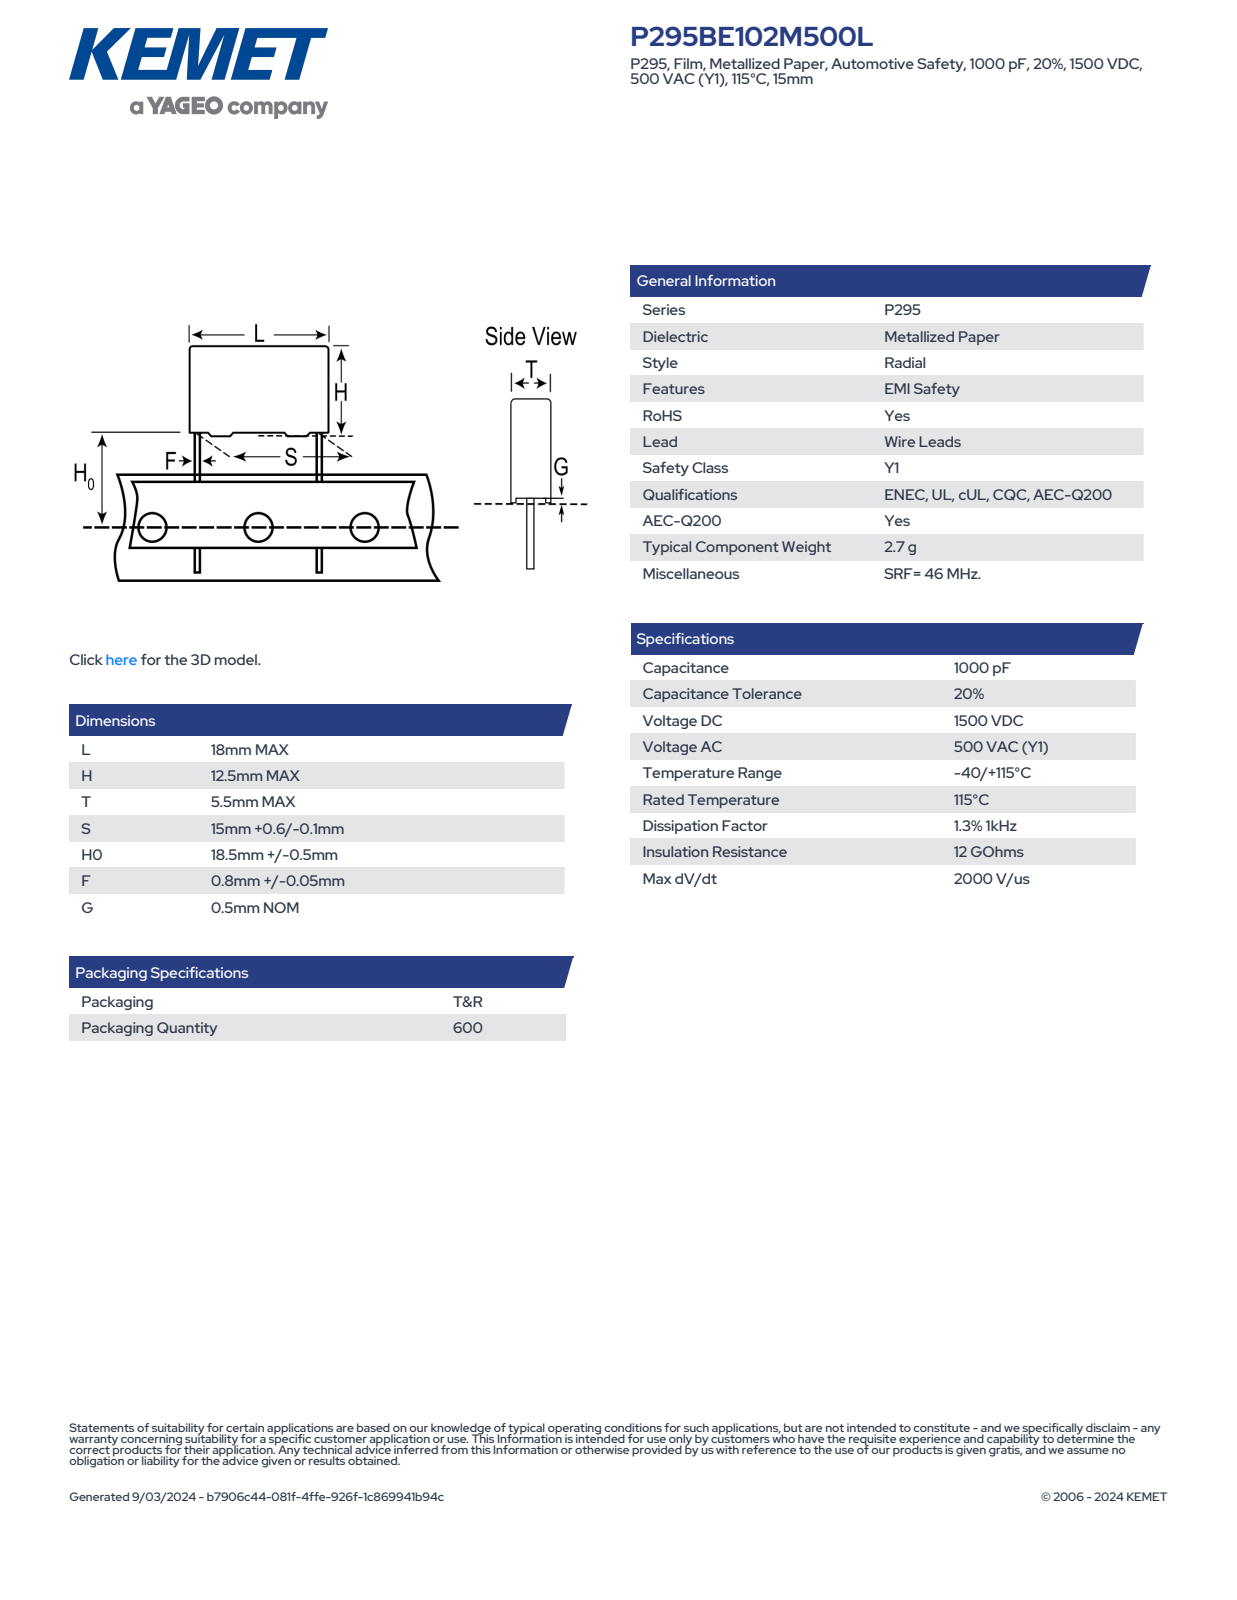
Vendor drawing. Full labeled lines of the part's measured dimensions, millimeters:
Part name (STEP PRODUCT): CFR_RBG_18X12.5X5.5_L18H12.5T5.5S15H019F0.85G0.5
STEP written by: SolidWorks 2014 (AUTOMOTIVE_DESIGN)
Units: millimetres
Bodies: 4 solids, 89 faces (81 planar, 8 cylindrical, 0 other)
Overall size (bounding box): 31.5 × 18 × 5.5
Volume: 1 210 mm³ · Surface area: 904 mm²
Round bosses / shafts (diameter × count): ⌀0.85 ×2
Partial cylindrical surfaces — rounded edges, fillets, slot ends (radius × count): R0.5 ×4
Main face-to-face distances: 5.5, 12, 18, 0.31, 5.19, 0.5, 12.5, 4.88, 19, 19.5
